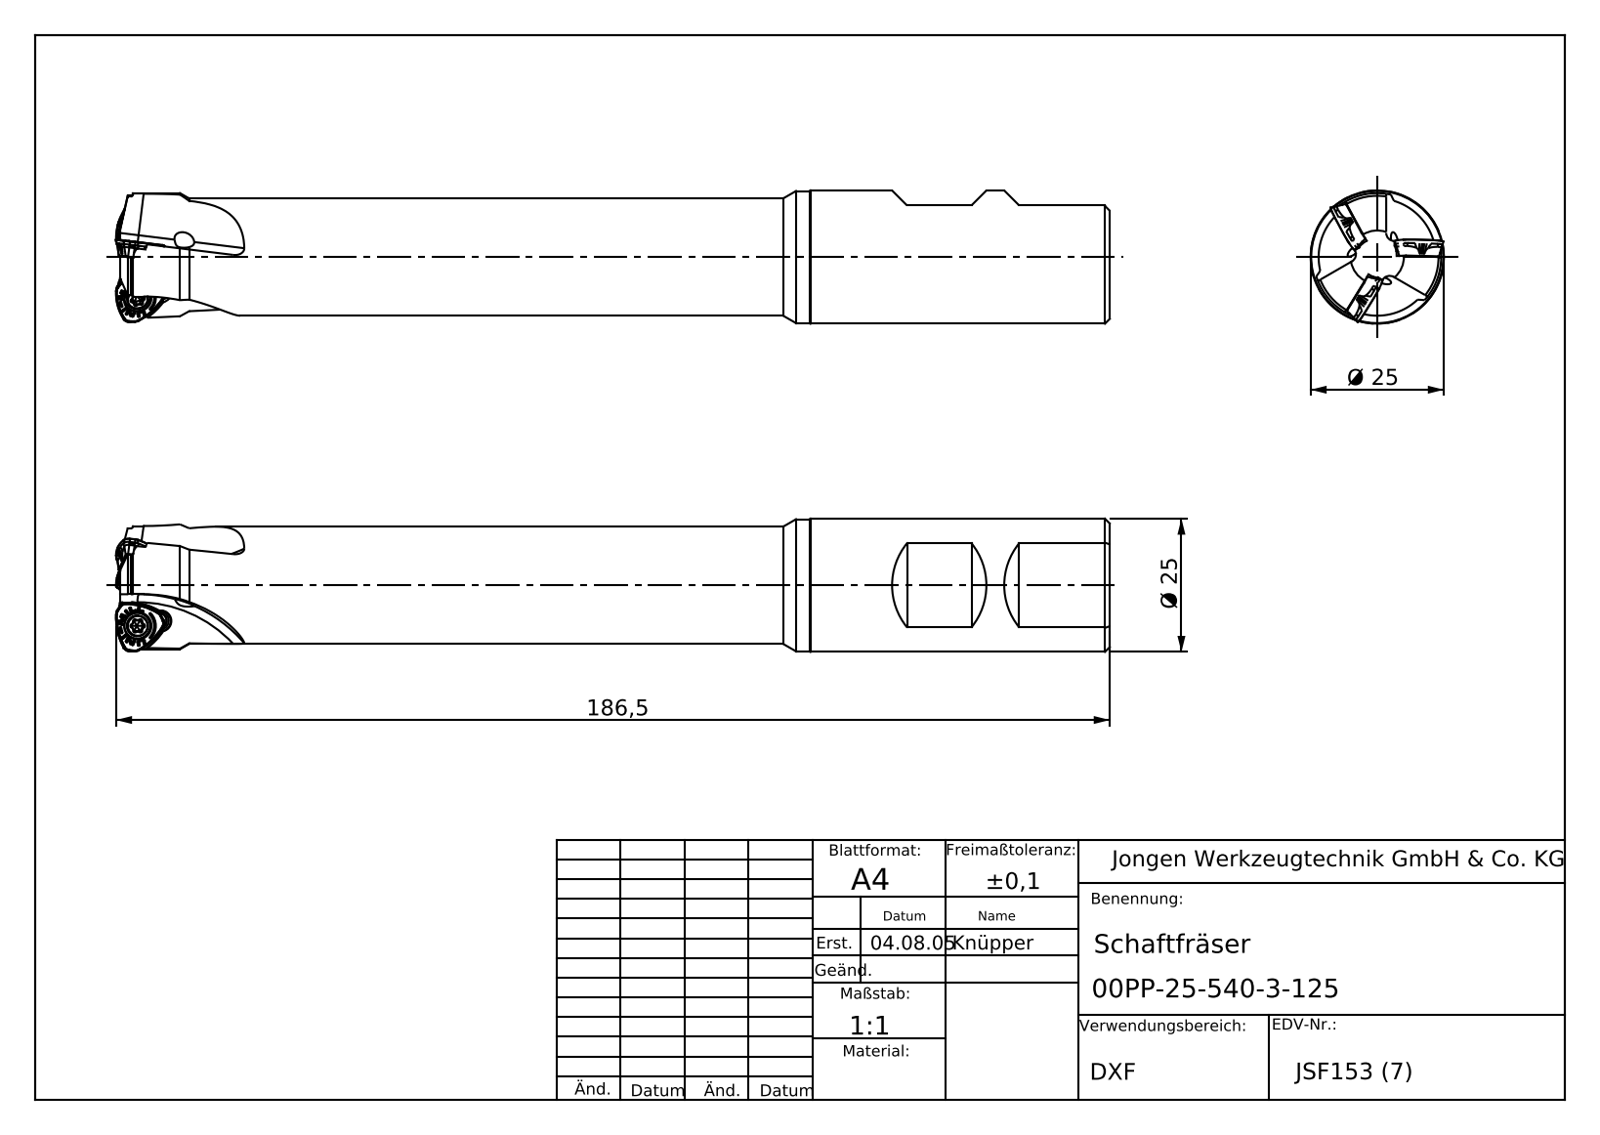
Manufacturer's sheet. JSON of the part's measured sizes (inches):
{"part_name": "00PP-25-540-3-125", "step_written_by": "SolidWorks 2013 (AUTOMOTIVE_DESIGN)", "units": "inches", "bodies": {"solids": 1, "faces": 103, "planar": 50, "cylindrical": 25, "other": 28}, "overall_size": [7.342, 0.985, 0.985], "volume_in3": 4.224, "surface_area_in2": 28.88, "round_holes": [[0.118, 3], [0.256, 1]], "round_bosses_or_shafts": [[0.984, 1], [0.976, 1], [0.866, 1]], "partial_cylinders_radius": [[0.059, 9], [0.077, 3], [1.036, 3], [0.472, 1]], "face_to_face_distances": [7.315, 0.586, 0.445, 1.031, 0.071, 0.039, 0.039, 0.04, 0.11, 0.11]}
